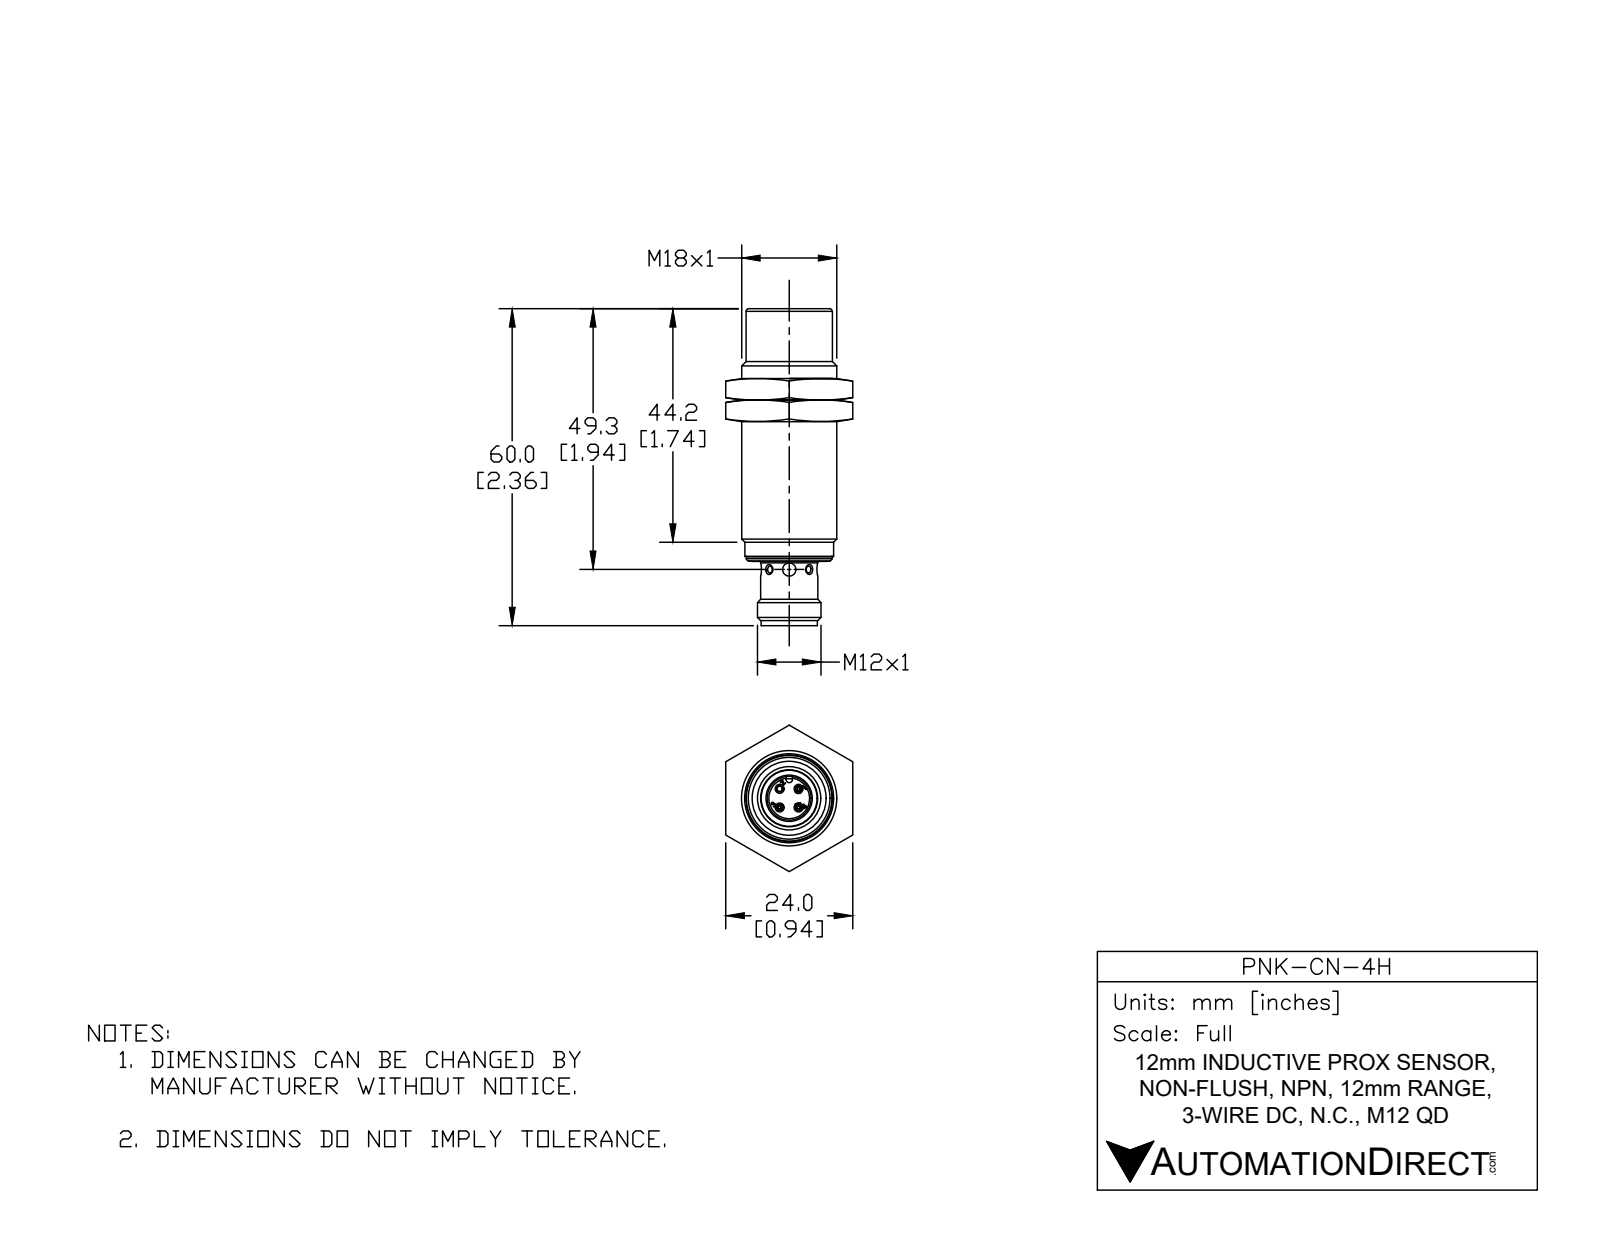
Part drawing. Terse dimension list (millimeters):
name: PNK-CN-4H
written by: SolidWorks 2017 (AUTOMOTIVE_DESIGN)
unit: mm
bodies: 1 solid, 1142 faces (751 planar, 150 cylindrical, 241 other)
size: 60 × 18 × 18
volume: 12 200 mm³; area: 9 458 mm²
holes: 3× ⌀1.1, 2× ⌀1, 2× ⌀2.5, 1× ⌀1, 1× ⌀1, 1× ⌀8.3, 1× ⌀10, 1× ⌀15.7, 1× ⌀16.1
bosses: 9× ⌀1, 1× ⌀18, 1× ⌀16.6, 1× ⌀16.2, 1× ⌀16.1, 1× ⌀15.6, 1× ⌀15.4, 1× ⌀15.2
rounds: 38× R0.1, 1× R0.6, 1× R0.8, 1× R4.1
face distances: 1, 0.6, 0.5, 47.5, 47.8, 47.2, 46.8, 46.9, 46.5, 59
hole spacings: 2.5, 3.5, 5
